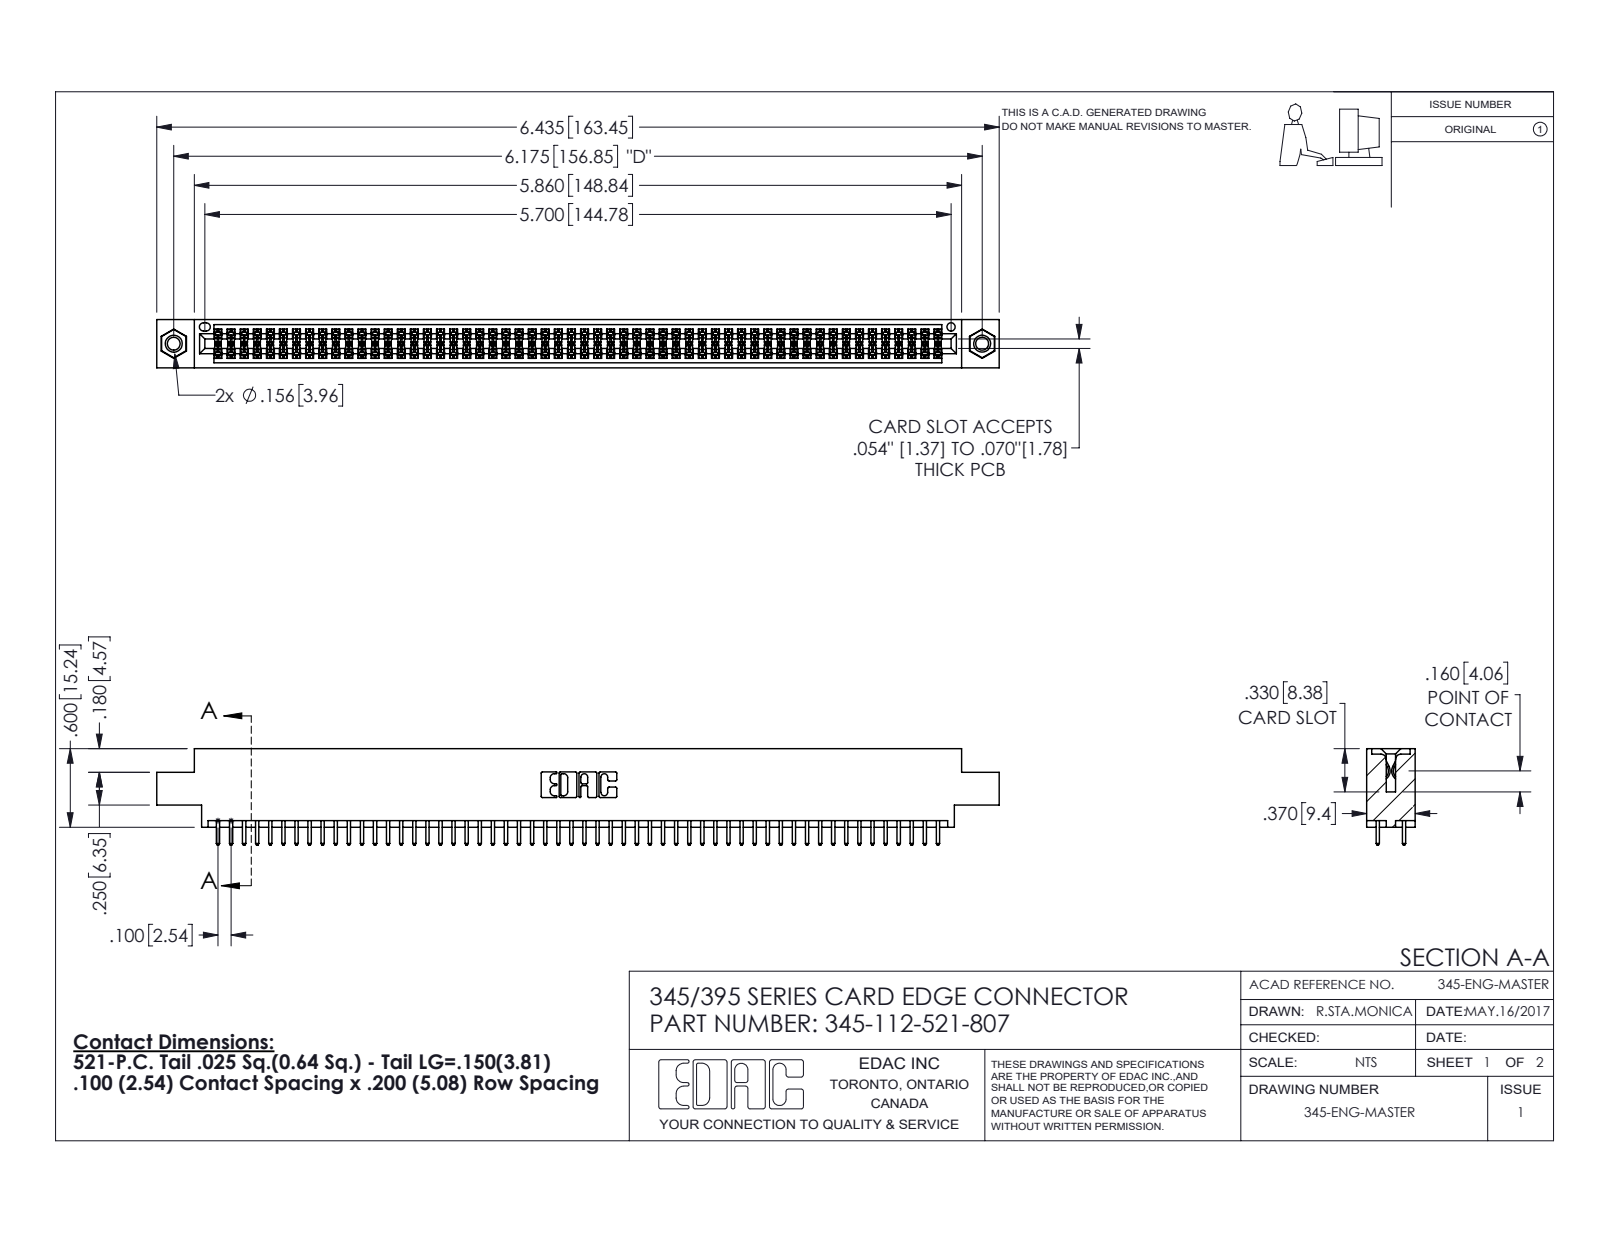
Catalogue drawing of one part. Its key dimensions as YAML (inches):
part_name: "345-250-001_345-250-005-103; 345-292-001_345-293-121; 345 Part_0.170 Offset - 0.156 Dia-TI; 345-112-521-807"
step_written_by: "SolidWorks 2016 (CONFIG_CONTROL_DESIGN)"
units: inches
bodies: {solids: 115, faces: 5790, planar: 3812, cylindrical: 1962, other: 16}
overall_size: [6.435, 0.737, 0.37]
volume: 0.966
surface_area: 36.51
round_holes:
  - {diameter: 0.098, count: 2}
  - {diameter: 0.125, count: 2}
  - {diameter: 0.156, count: 2}
  - {diameter: 0.064, count: 1}
round_bosses_or_shafts:
  - {diameter: 0.155, count: 2}
partial_cylinders:
  - {radius: 0.006, count: 168}
  - {radius: 0.01, count: 112}
  - {radius: 0.01, count: 22}
  - {radius: 0.007, count: 6}
  - {radius: 0.031, count: 6}
  - {radius: 0.026, count: 3}
  - {radius: 0.014, count: 2}
  - {radius: 0.019, count: 2}
face_to_face_distances: [0.072, 0.298, 0.2, 0.37, 0.098, 0.272, 0.025, 0.225, 0.175, 0.149]
hole_center_spacings: [0.27, 5.939, 6.175]
